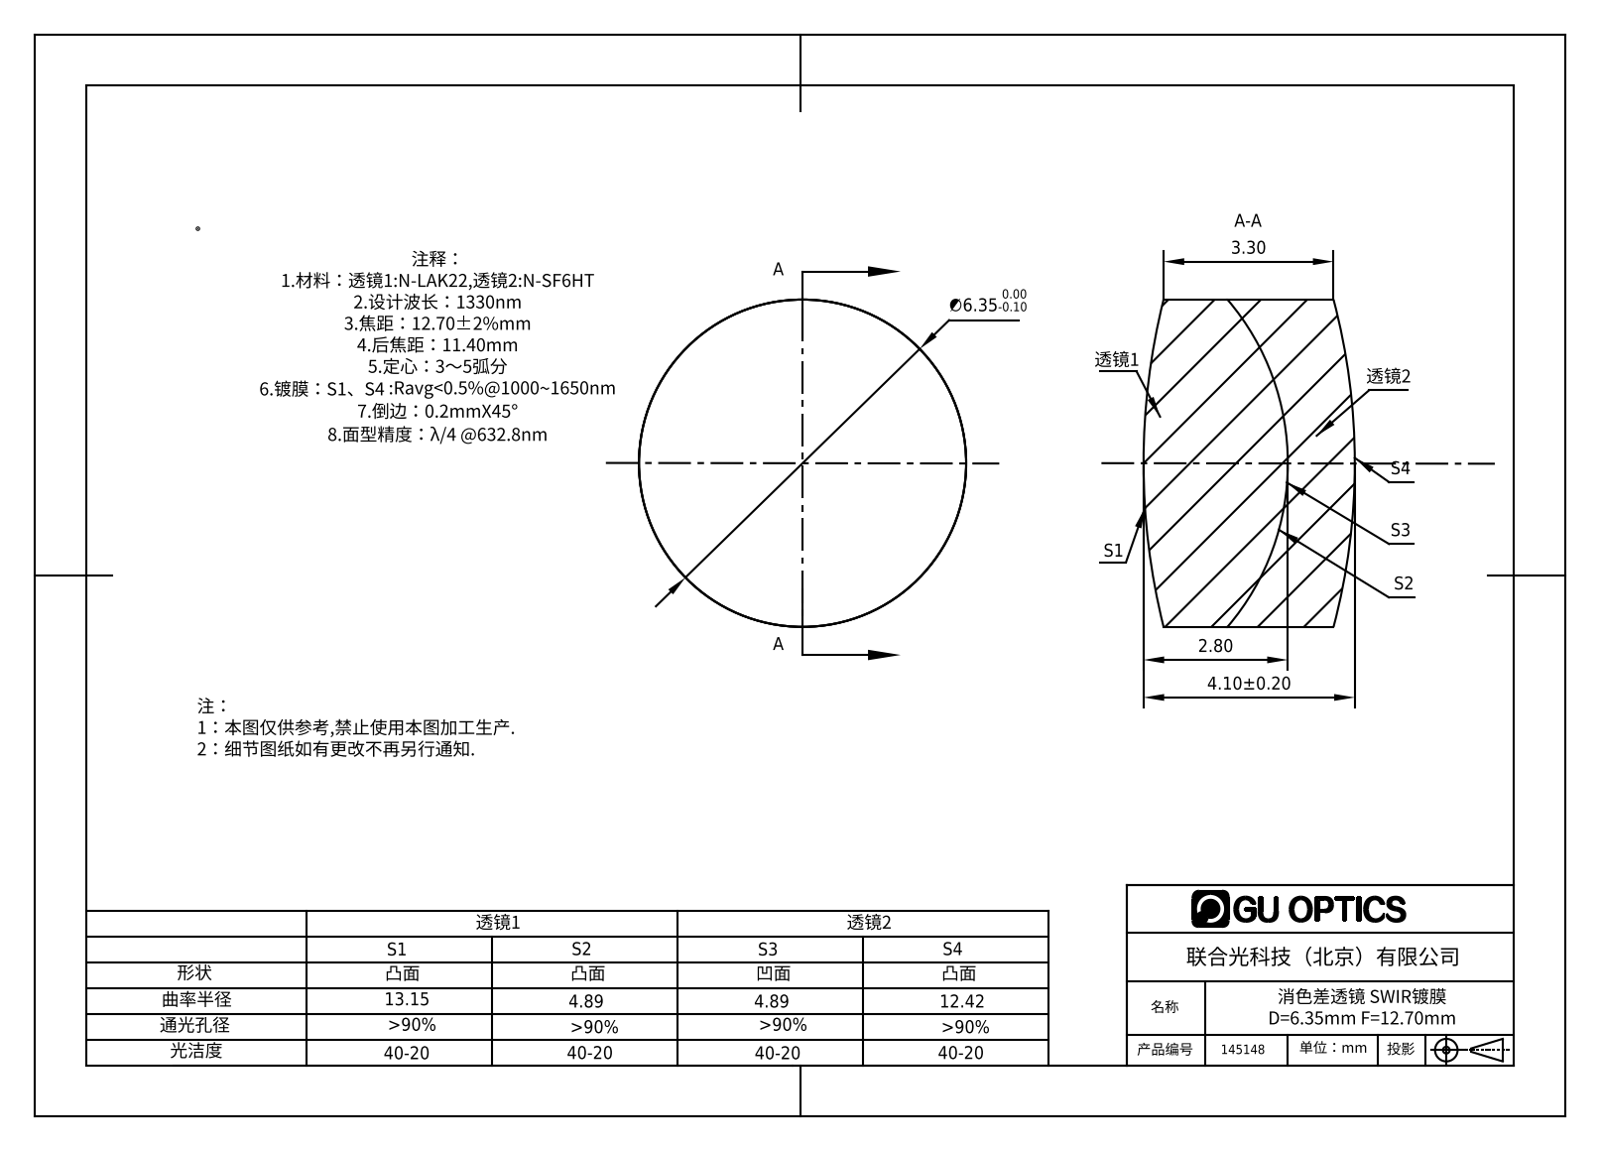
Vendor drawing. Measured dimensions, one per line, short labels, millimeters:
name: 145148
written by: SolidWorks 2016 (AUTOMOTIVE_DESIGN)
unit: mm
bodies: 2 solids, 12 faces (0 planar, 4 cylindrical, 8 other)
size: 6.35 × 6.35 × 4.1
volume: 117 mm³; area: 202 mm²
bosses: 1× ⌀6.35
